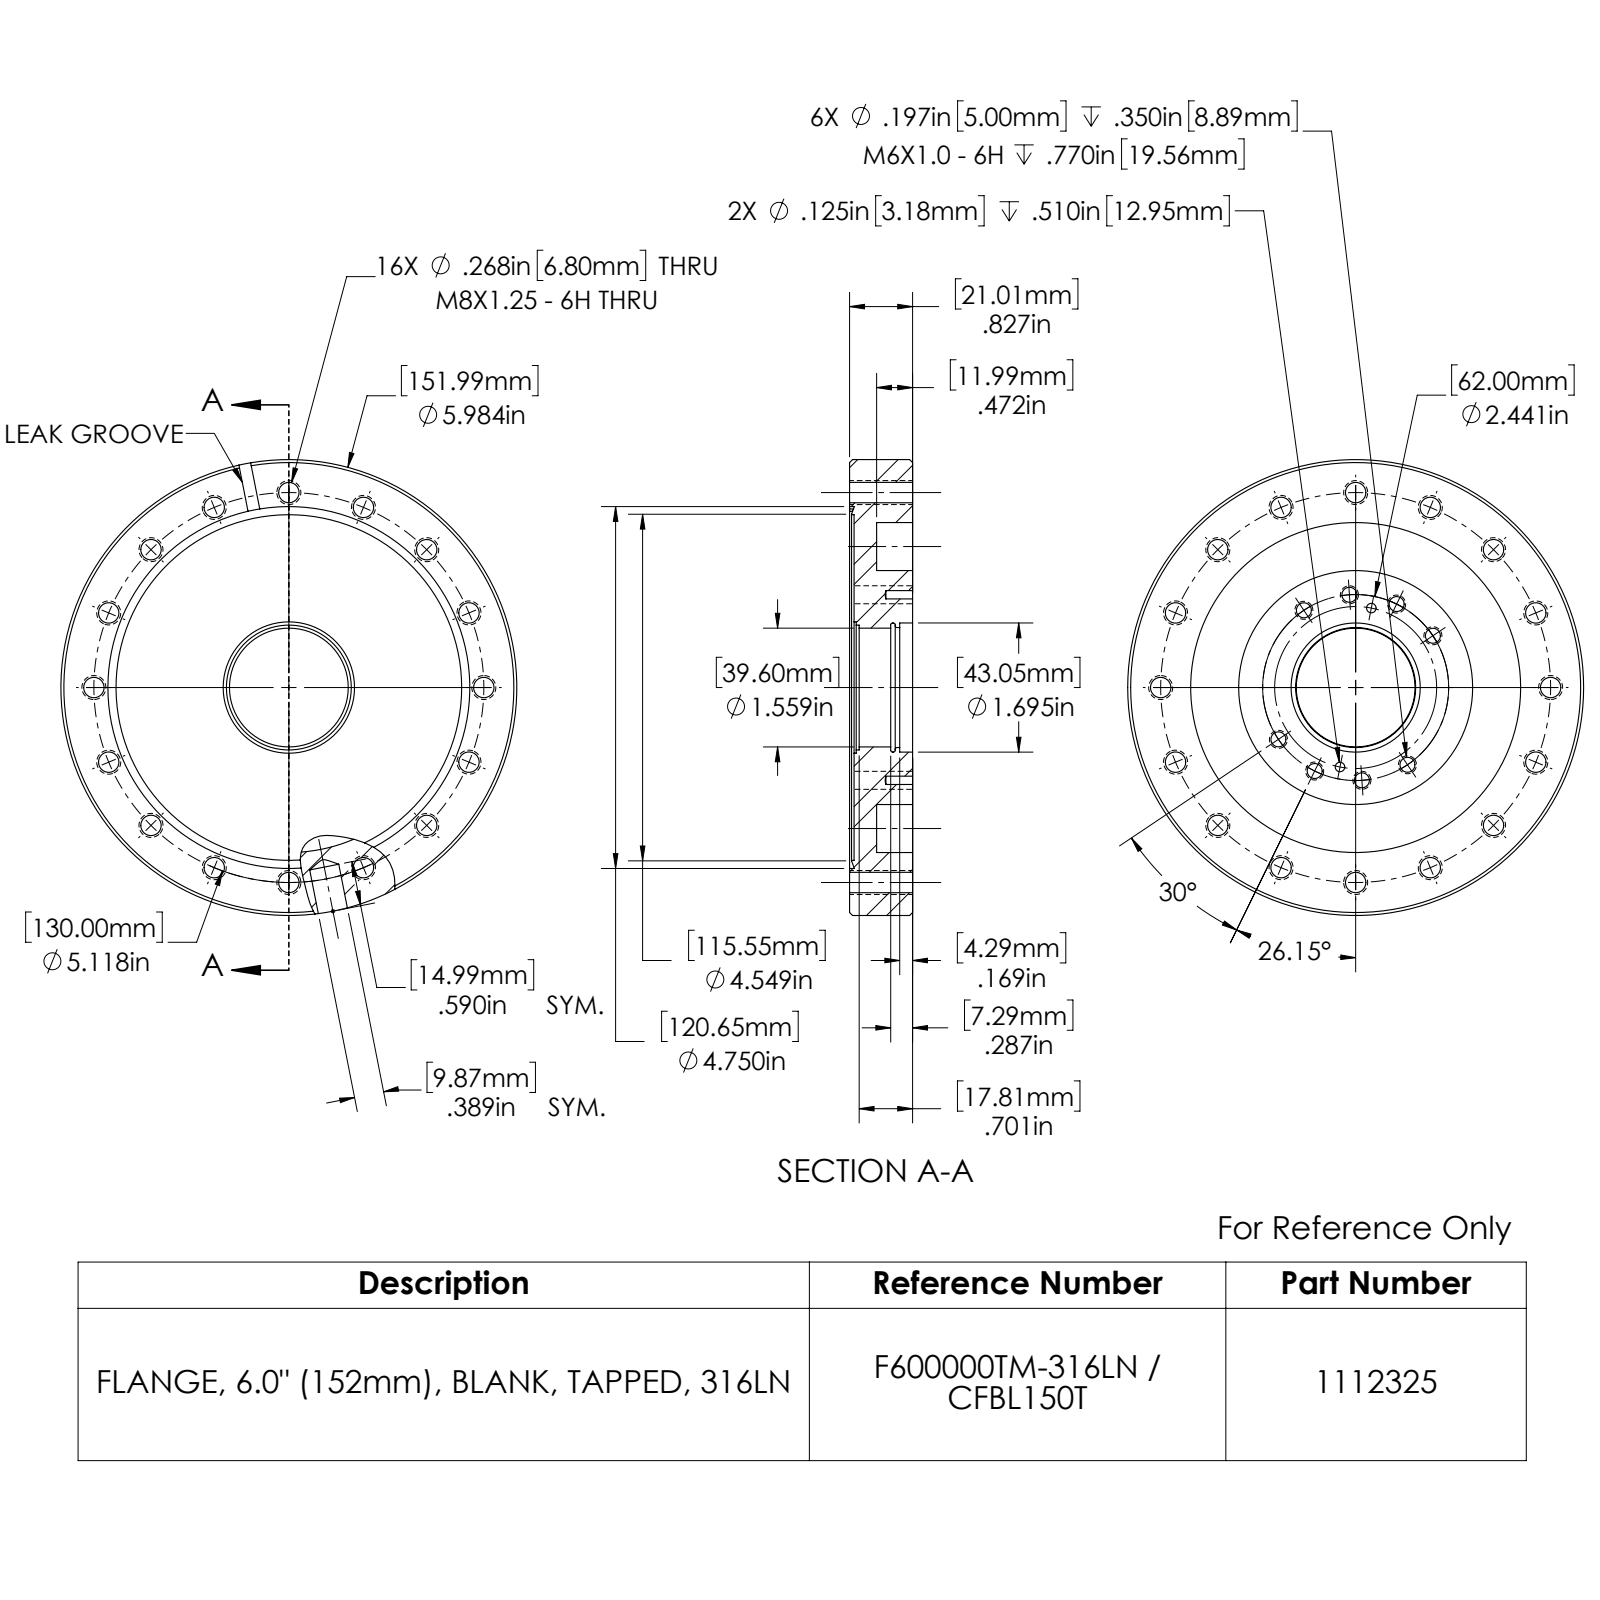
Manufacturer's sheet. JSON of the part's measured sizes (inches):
{"part_name": "1112325_A", "step_written_by": "SolidWorks 2022 (CONFIG_CONTROL_DESIGN)", "units": "inches", "bodies": {"solids": 1, "faces": 138, "planar": 19, "cylindrical": 78, "other": 41}, "overall_size": [5.984, 5.984, 0.827], "volume_in3": 16.16, "surface_area_in2": 97.1, "round_holes": [[0.268, 16], [0.197, 8], [0.125, 2], [0.394, 2], [1.559, 1], [1.575, 1], [1.639, 1], [1.693, 1], [1.695, 1], [1.724, 1], [4.331, 1], [4.75, 1]], "round_bosses_or_shafts": [[5.984, 1], [3.071, 1]], "partial_cylinders_radius": [[0.787, 2]], "face_to_face_distances": [0.768, 0.059, 0.827, 0.472, 0.296, 0.355, 0.54, 0.599, 0.118, 0.169], "hole_center_spacings": [0.998, 2.559, 2.843, 3.619, 4.256, 4.728, 5.02, 1.959]}
